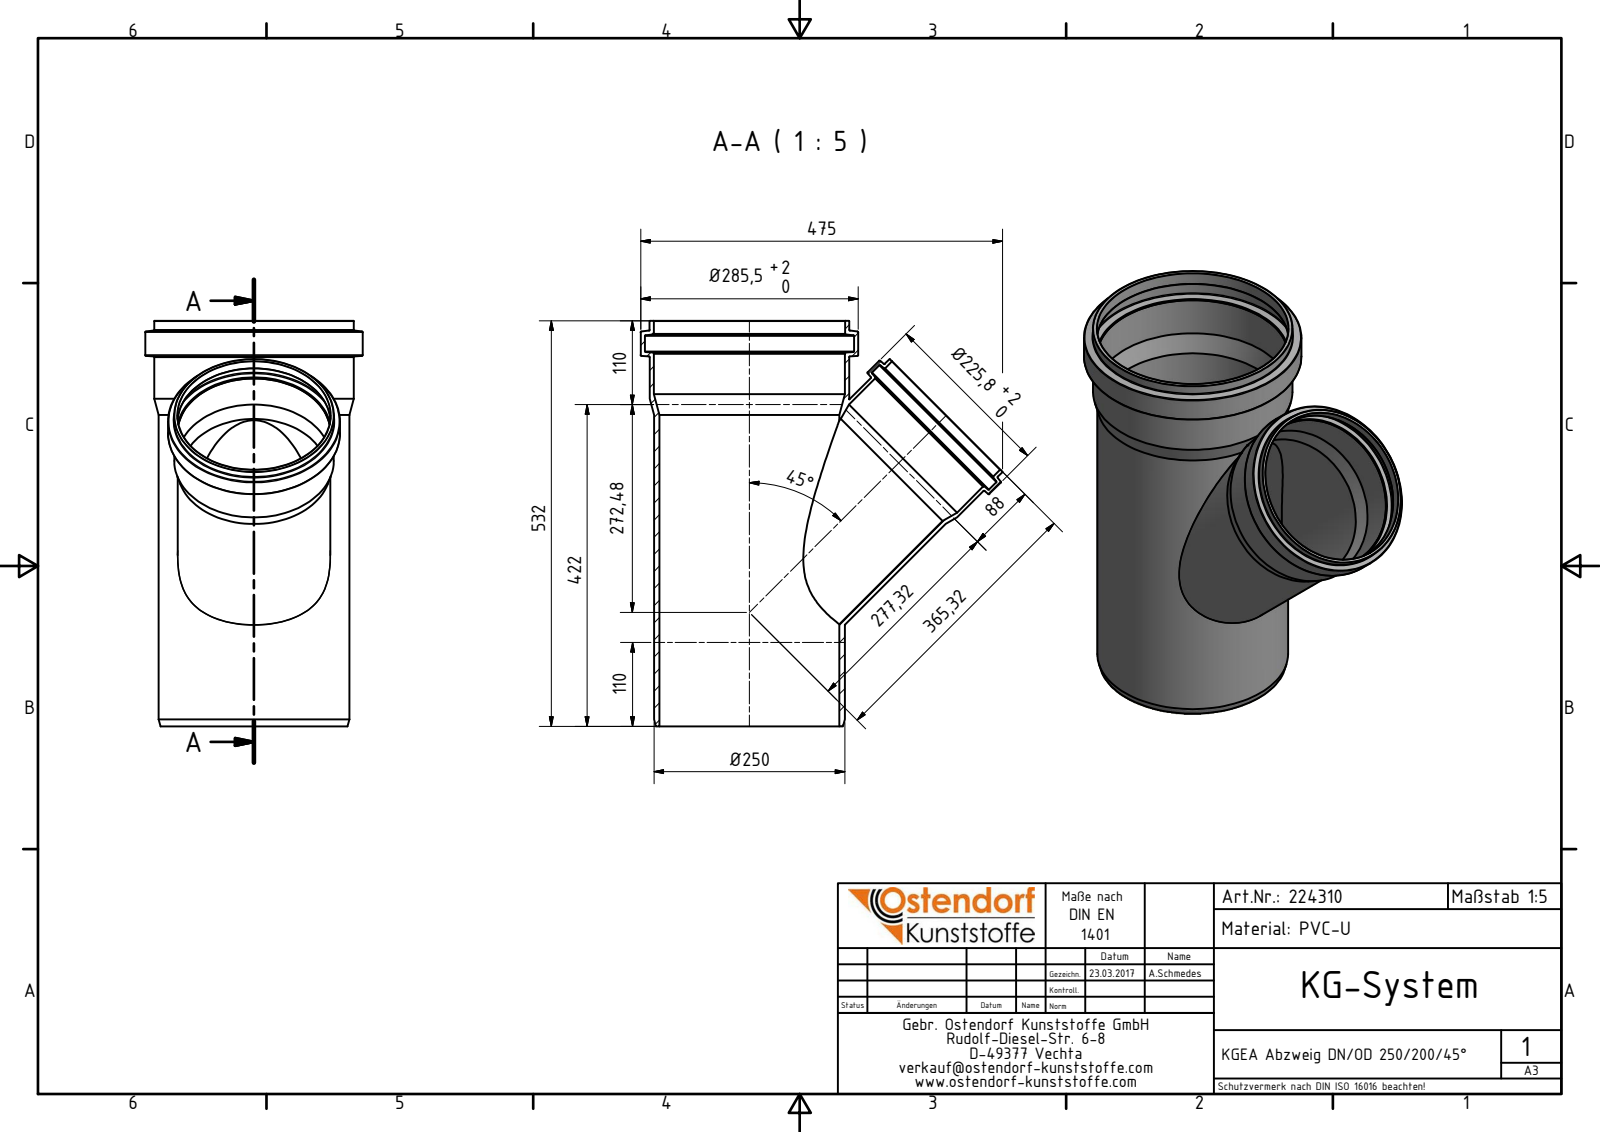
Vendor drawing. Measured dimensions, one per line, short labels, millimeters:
name: 224310 KGEA Abzweig DN_OD 250_200_45°
written by: Autodesk Inventor 2016 (AUTOMOTIVE_DESIGN)
unit: mm
bodies: 1 solid, 62 faces (5 planar, 18 cylindrical, 39 other)
size: 532 × 475 × 285.5
volume: 3 331 000 mm³; area: 1 079 000 mm²
holes: 2× ⌀200.9, 1× ⌀189.3, 1× ⌀200.6, 1× ⌀217, 1× ⌀236.3, 1× ⌀250.8, 1× ⌀251.1, 1× ⌀274.5
bosses: 1× ⌀285.5, 1× ⌀262.1, 1× ⌀261.8, 1× ⌀250.5, 1× ⌀225.8, 1× ⌀209.7, 1× ⌀209.4, 1× ⌀200.5
face distances: 532, 488.77, 43.23, 31.76
